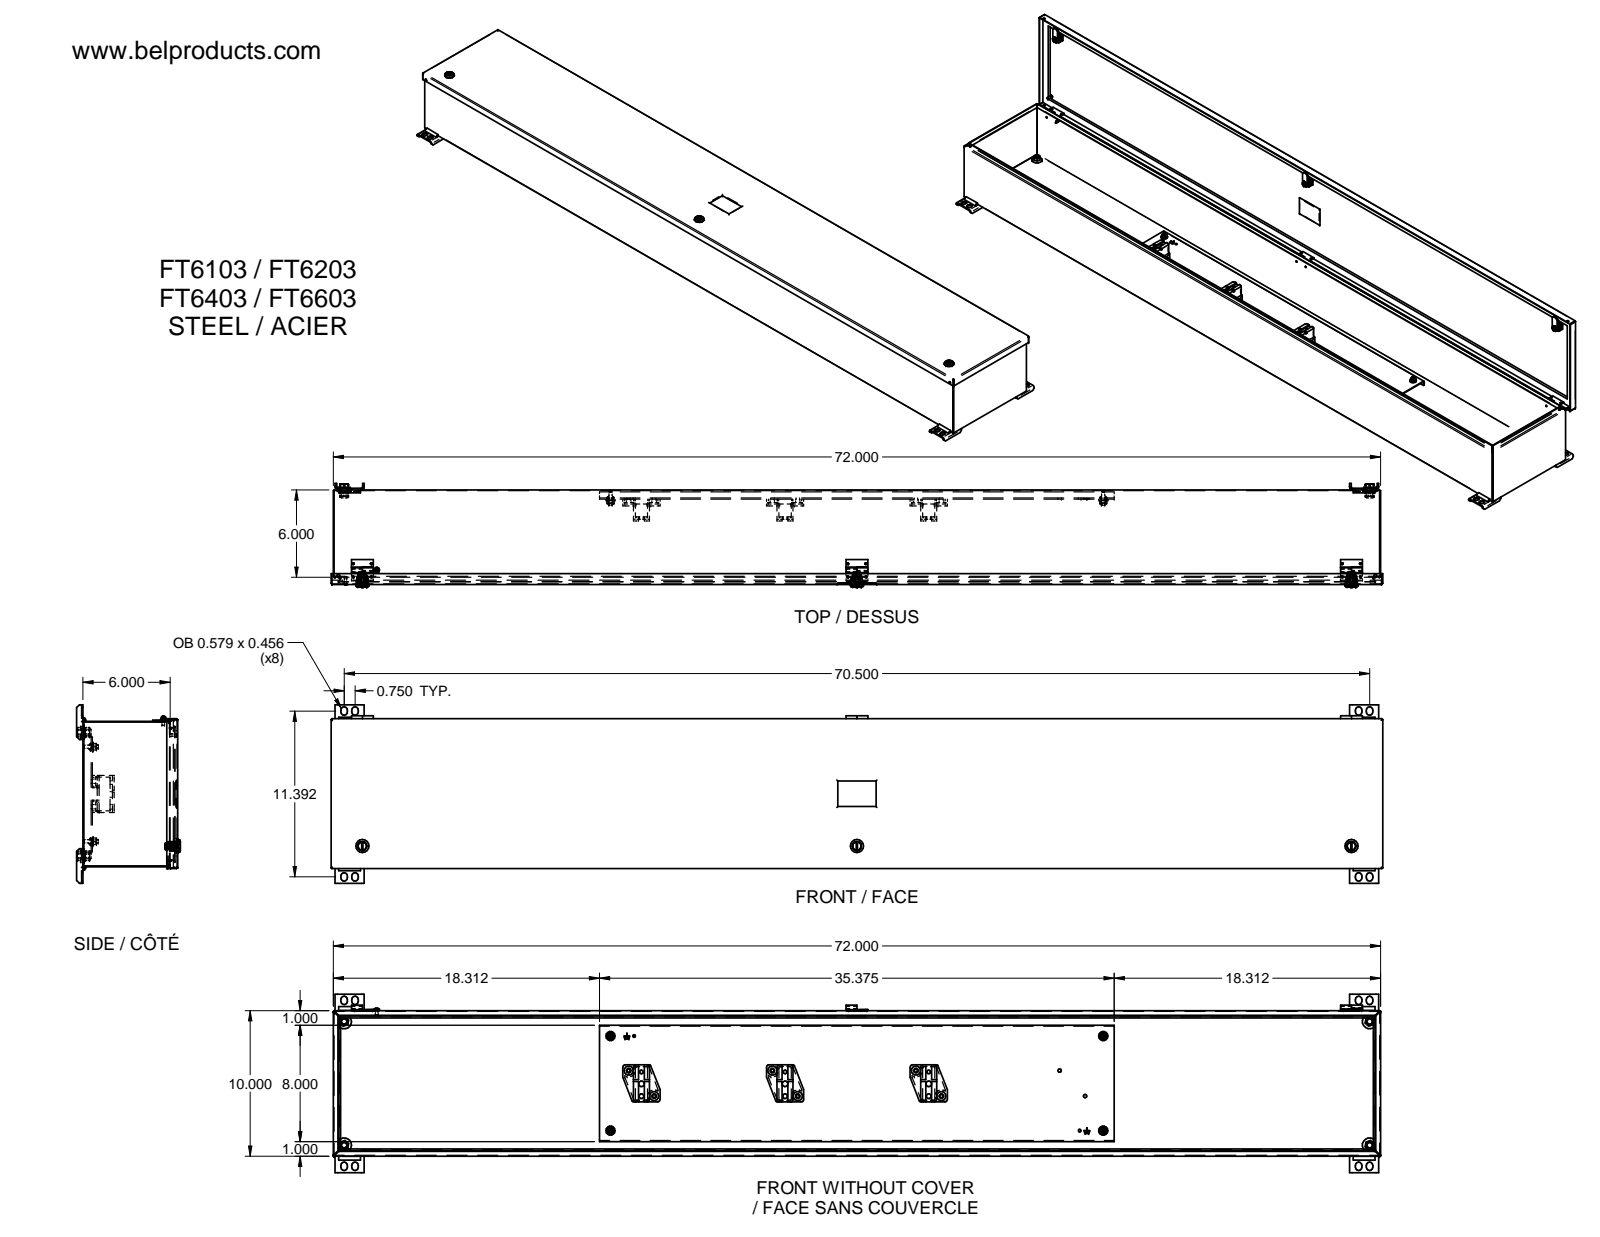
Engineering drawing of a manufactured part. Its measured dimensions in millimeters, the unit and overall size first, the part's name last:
Units: millimetres
Overall size (bounding box): 1836.42 × 311.56 × 180.97
Round holes (diameter × count): ⌀3.16 ×12, ⌀3.3 ×12, ⌀5.99 ×8, ⌀9.53 ×8, ⌀11.58 ×8, ⌀6.35 ×7, ⌀7.92 ×6, ⌀15.88 ×6, ⌀3.17 ×5, ⌀7.14 ×4, ⌀9.02 ×4, ⌀10.31 ×4
Round bosses / shafts (diameter × count): ⌀3.17 ×12, ⌀3.02 ×5, ⌀20.62 ×4, ⌀15.88 ×4, ⌀5.56 ×4, ⌀0.79 ×4, ⌀22.86 ×3, ⌀22.61 ×3
Partial cylindrical surfaces — rounded edges, fillets, slot ends (radius × count): R9.53 ×32, R0.25 ×24, R4.76 ×22, R0.81 ×16, R5.79 ×16, R2.34 ×14, R1.46 ×12, R1.52 ×8
Main face-to-face distances: 1.52, 252.48, 1.53, 163.93, 165.46, 162.41, 163.94, 250.96, 254, 1.91
Hole centre spacings: 250.82, 501.65, 250.83, 863.6, 23.03, 62.86, 31.75, 211.1
Volume: 3 695 000 mm³ · Surface area: 4 217 000 mm²
Bodies: 81 solids, 2943 faces (1705 planar, 585 cylindrical, 653 other)
Part name (STEP PRODUCT): 0.375 DIA; CAOUTCHOUC; METAL; LOCK AVEC TOURNEVIS TYPE 4-12 SANS CAME-oa8 (+8 more)
STEP written by: Unknown (AUTOMOTIVE_DESIGN)
